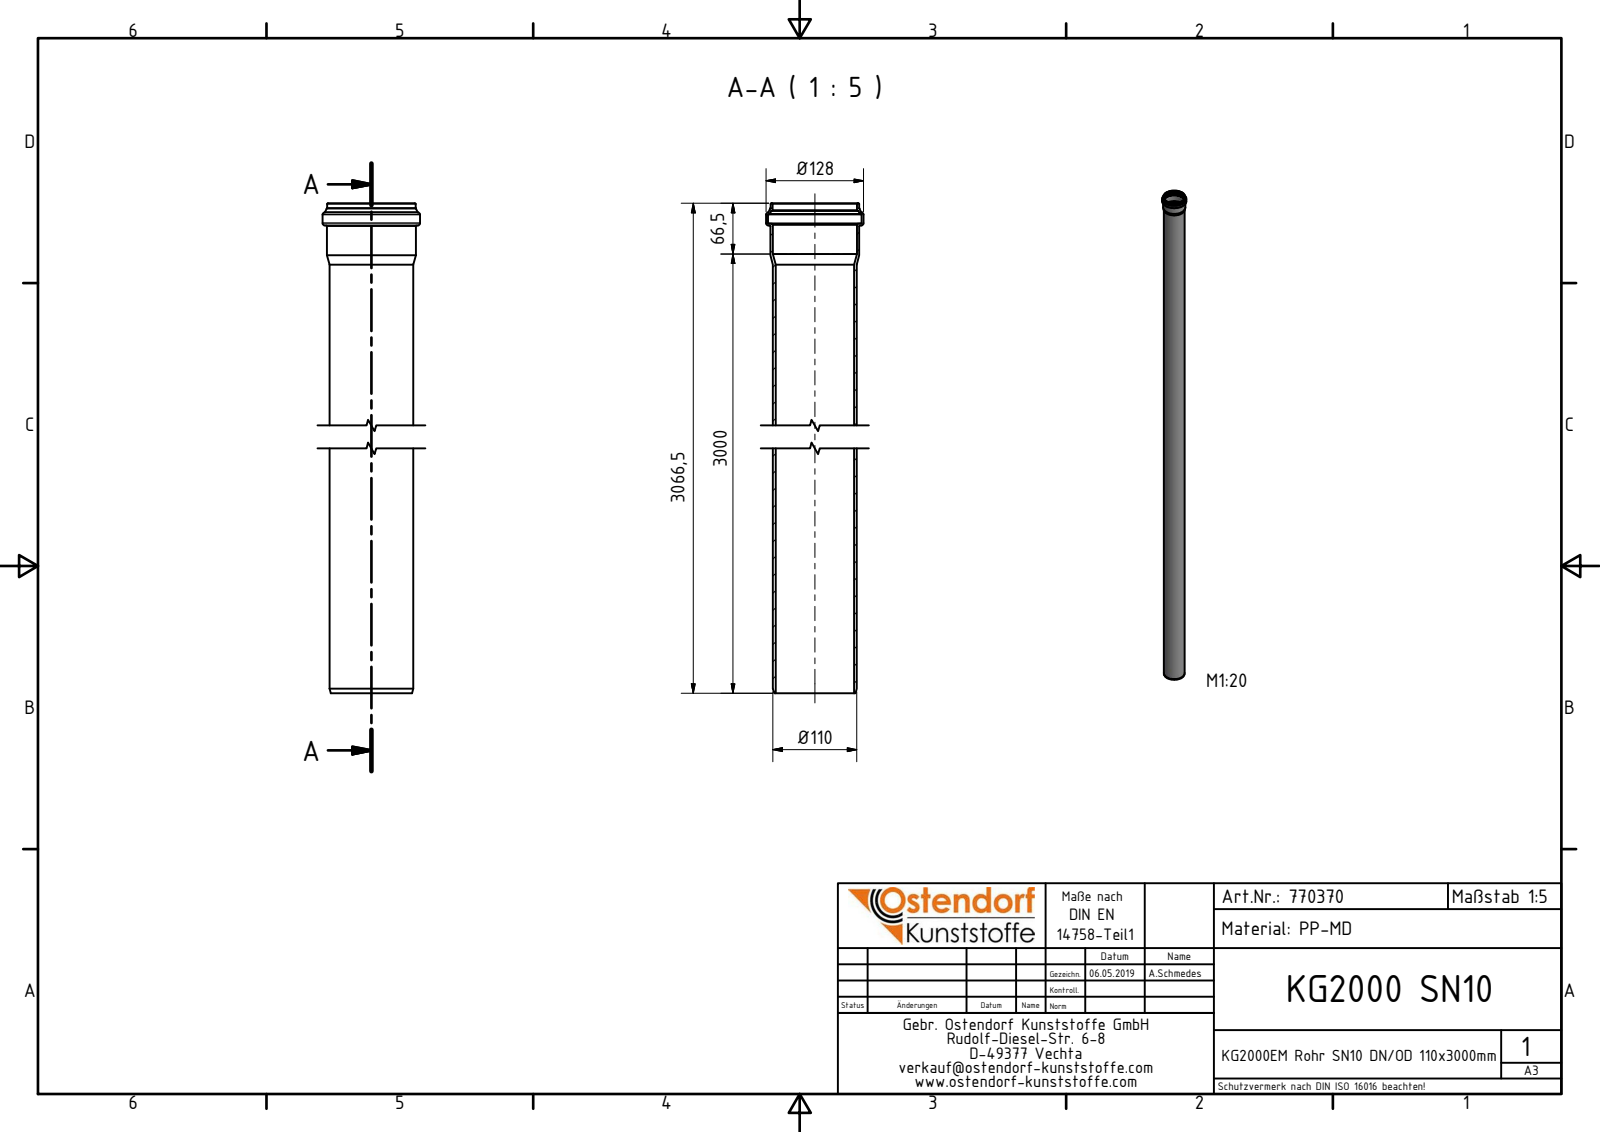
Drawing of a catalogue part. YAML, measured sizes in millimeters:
part_name: "770370 KG2000EM Rohr SN10 DN-OD110x3000"
step_written_by: "Autodesk Inventor 2016 (AUTOMOTIVE_DESIGN)"
units: millimeters
bodies: {solids: 1, faces: 37, planar: 6, cylindrical: 9, other: 22}
overall_size: [3066.5, 128, 128]
volume: 3609000
surface_area: 2063000
round_holes:
  - {diameter: 102.96, count: 1}
  - {diameter: 110.5, count: 1}
  - {diameter: 110.9, count: 1}
  - {diameter: 122.8, count: 1}
round_bosses_or_shafts:
  - {diameter: 128, count: 1}
  - {diameter: 116.7, count: 1}
  - {diameter: 116.1, count: 1}
  - {diameter: 110, count: 1}
face_to_face_distances: [3037.4, 3066.5, 29.1, 3038.22, 0.82, 28.28, 3054.5, 17.1, 16.28, 12]
